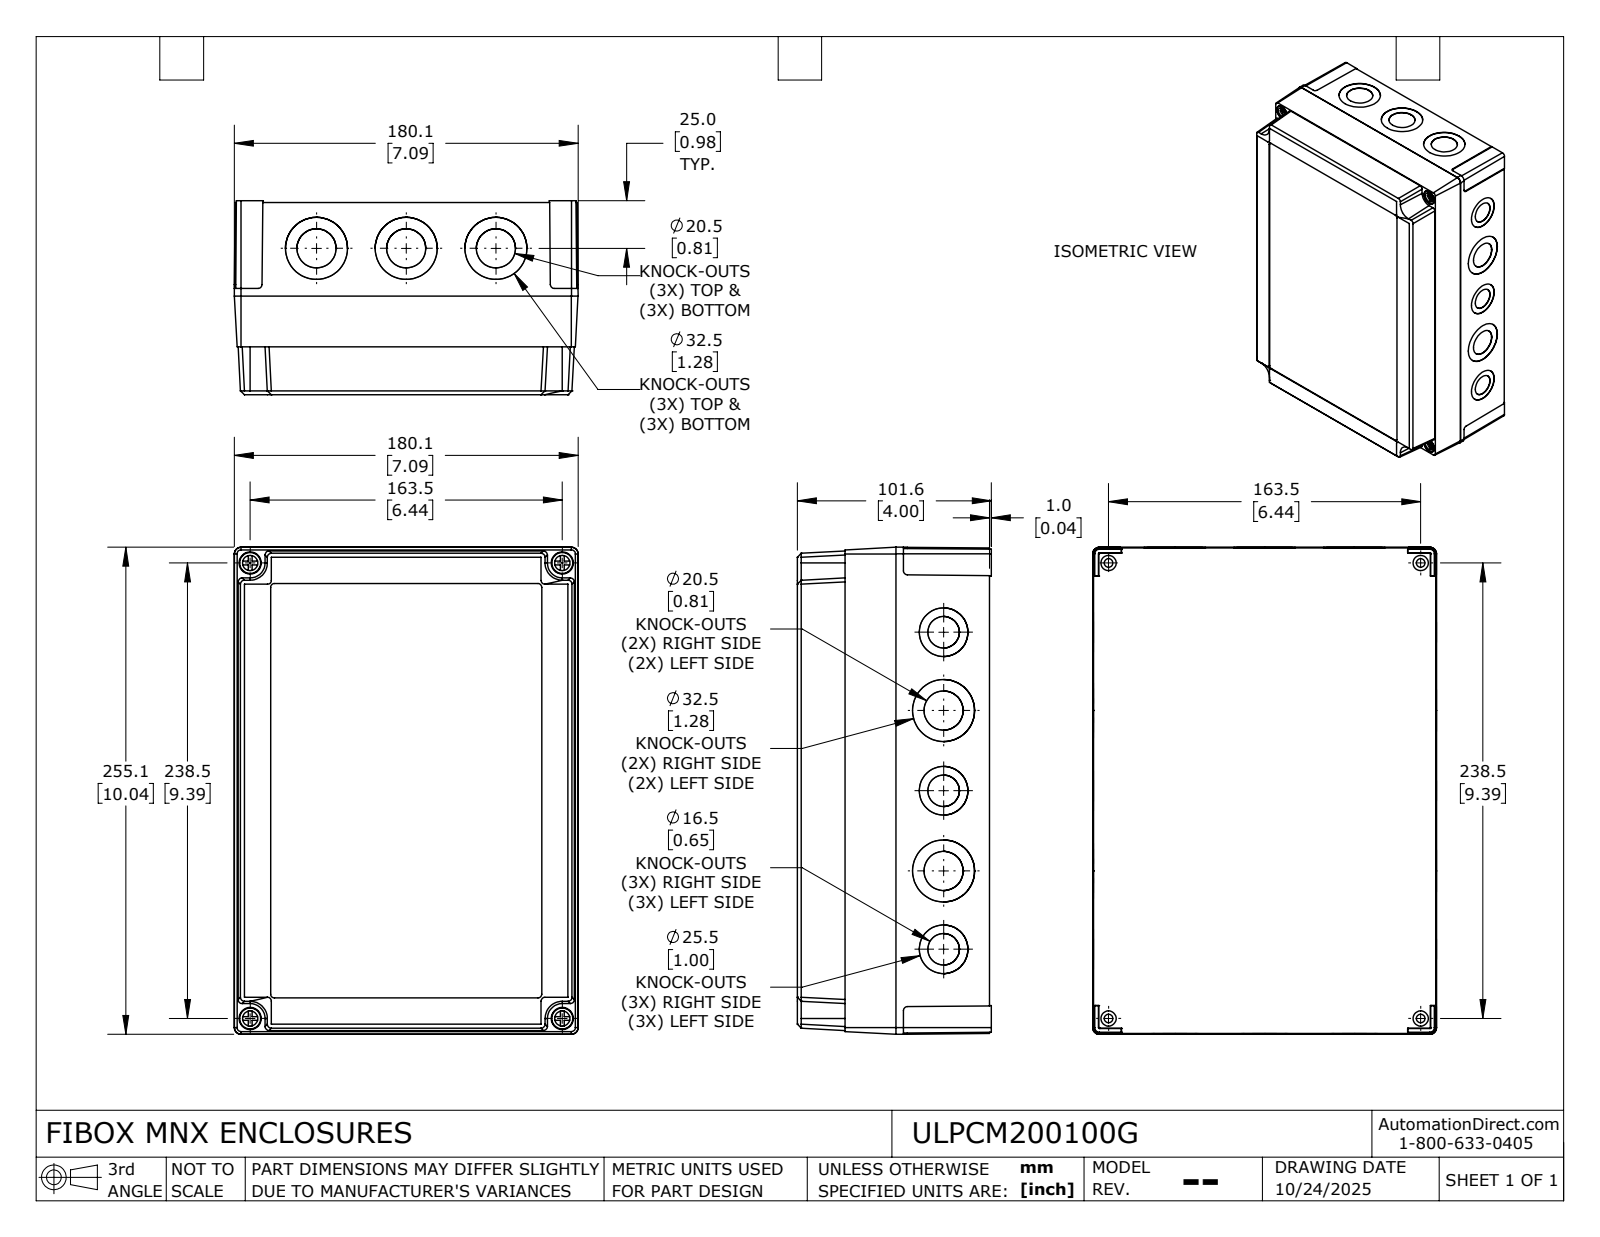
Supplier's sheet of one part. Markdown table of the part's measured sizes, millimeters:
| quantity | value |
| --- | --- |
| part name | ULPCM200100G |
| STEP written by | SolidWorks 2024 (AUTOMOTIVE_DESIGN) |
| units | millimeters |
| bodies | 6 solids, 725 faces (383 planar, 280 cylindrical, 62 other) |
| overall size | 255.1 × 180.1 × 101.6 |
| volume | 511 800 mm³ |
| surface area | 362 600 mm² |
| round holes (diameter × count) | 3.2 × 20, 4 × 20, 20.5 × 10, 32.5 × 10, 16.5 × 6, 25.5 × 6, 4.5 × 4, 8 × 4, 11.6 × 4 |
| round bosses / shafts (diameter × count) | 8 × 16, 11 × 4, 7.2 × 4, 7 × 4 |
| partial cylindrical surfaces (radius × count) | 2 × 8, 2.1 × 8, 2.8 × 6, 1.1 × 4, 5 × 4, 1.2 × 2 |
| main face-to-face distances | 98, 3, 95, 100.1, 97.1, 2.1, 4.2, 2, 1.4, 0.6 |
| hole center spacings | 125, 49.3, 128.2, 20.6, 22.1, 26.6, 33.9, 38.3 |
